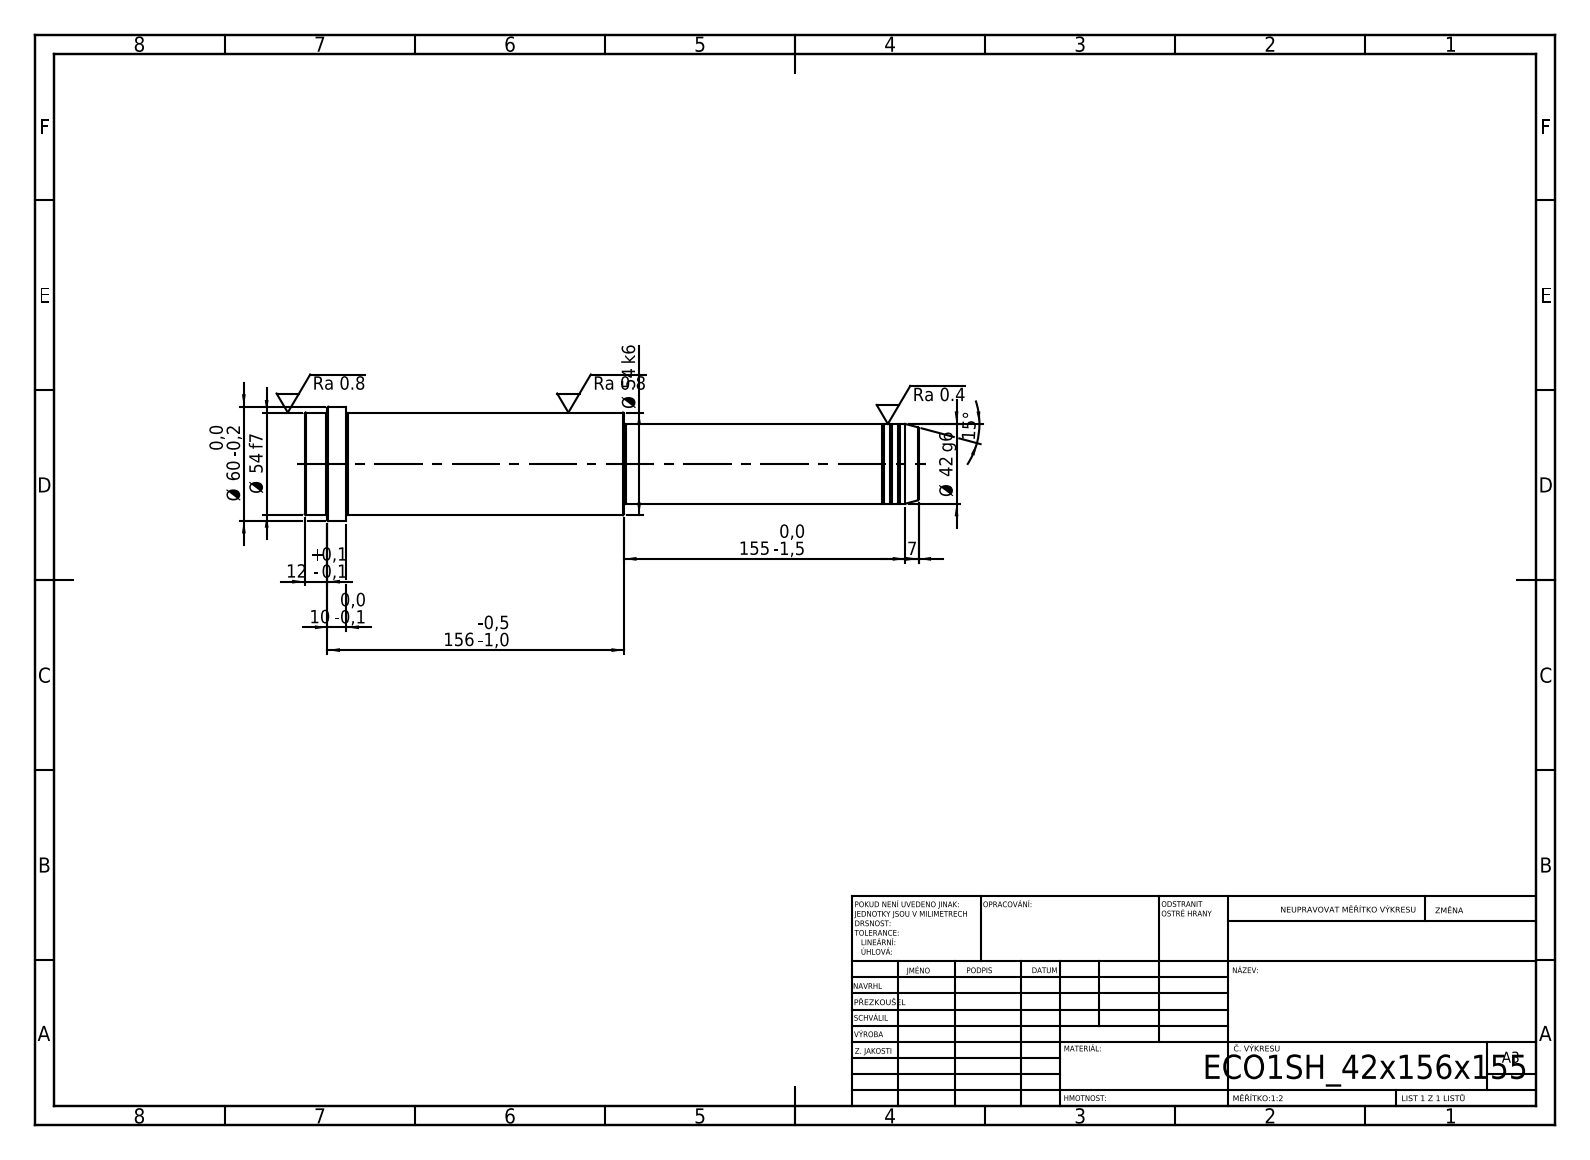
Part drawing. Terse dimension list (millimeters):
written by: SolidWorks 2019 (CONFIG_CONTROL_DESIGN)
unit: mm
bodies: 1 solid, 52 faces (6 planar, 16 cylindrical, 30 other)
size: 323 × 60 × 60
volume: 603 612 mm³; area: 54 911 mm²
bosses: 1× ⌀60, 1× ⌀54, 1× ⌀42, 1× ⌀41
face distances: 323, 155, 168, 301, 146, 22, 311, 156, 10, 12
